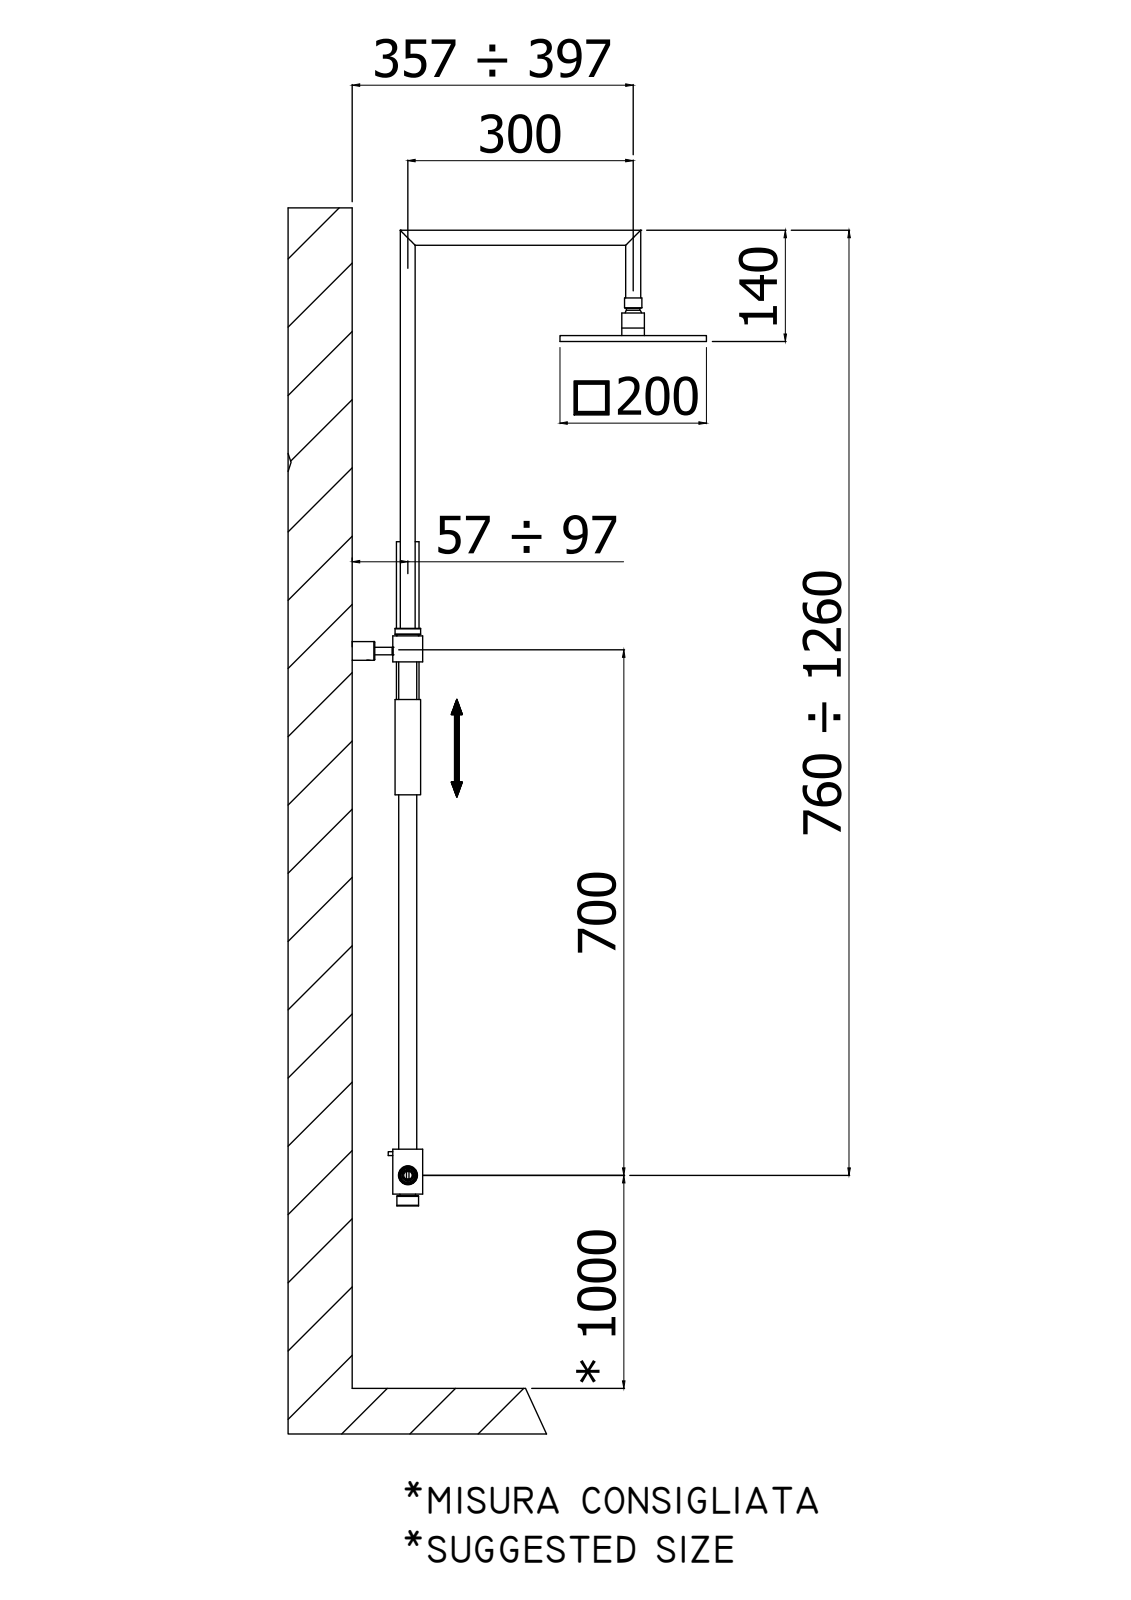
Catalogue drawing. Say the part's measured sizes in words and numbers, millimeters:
The part is named "ZCOL615CR". Its 3-D file was written by "CREO PARAMETRIC BY PTC INC, 2020044 (CONFIG_CONTROL_DESIGN)". It is 7 solids with 5803 faces: 966 planar, 1073 cylindrical and 3764 other. Overall it measures 1035 by 480.1 by 208.19 millimeters. Its volume is 693 817 cubic millimeters and its surface area 513 158 square millimeters. Round holes: 100 of diameter 1.5, 100 of diameter 1.7, 13 of diameter 7, 12 of diameter 2.5, 12 of diameter 5.1, 12 of diameter 6, 5 of diameter 5, 3 of diameter 3.3, 3 of diameter 17, 2 of diameter 4.5, 2 of diameter 8.5, 2 of diameter 10. Round bosses or shafts: 101 of diameter 10, 12 of diameter 5, 11 of diameter 2, 4 of diameter 20, 2 of diameter 24, 2 of diameter 21, 1 of diameter 34, 1 of diameter 31.8. Partial cylindrical surfaces (rounded edges, fillets, slot ends): 12 of radius 20, 8 of radius 1, 4 of radius 12, 2 of radius 4, 1 of radius 6.75, 1 of radius 9.75, 1 of radius 12.1, 1 of radius 12.3. The main face-to-face distances are 8.5, 7.5, 1, 7, 6, 1.5, 3, 37, 25, 22. The hole center spacings are 16.3, 36.45, 23.05, 51.55, 32.6, 67.21, 48.9, 65.2.
